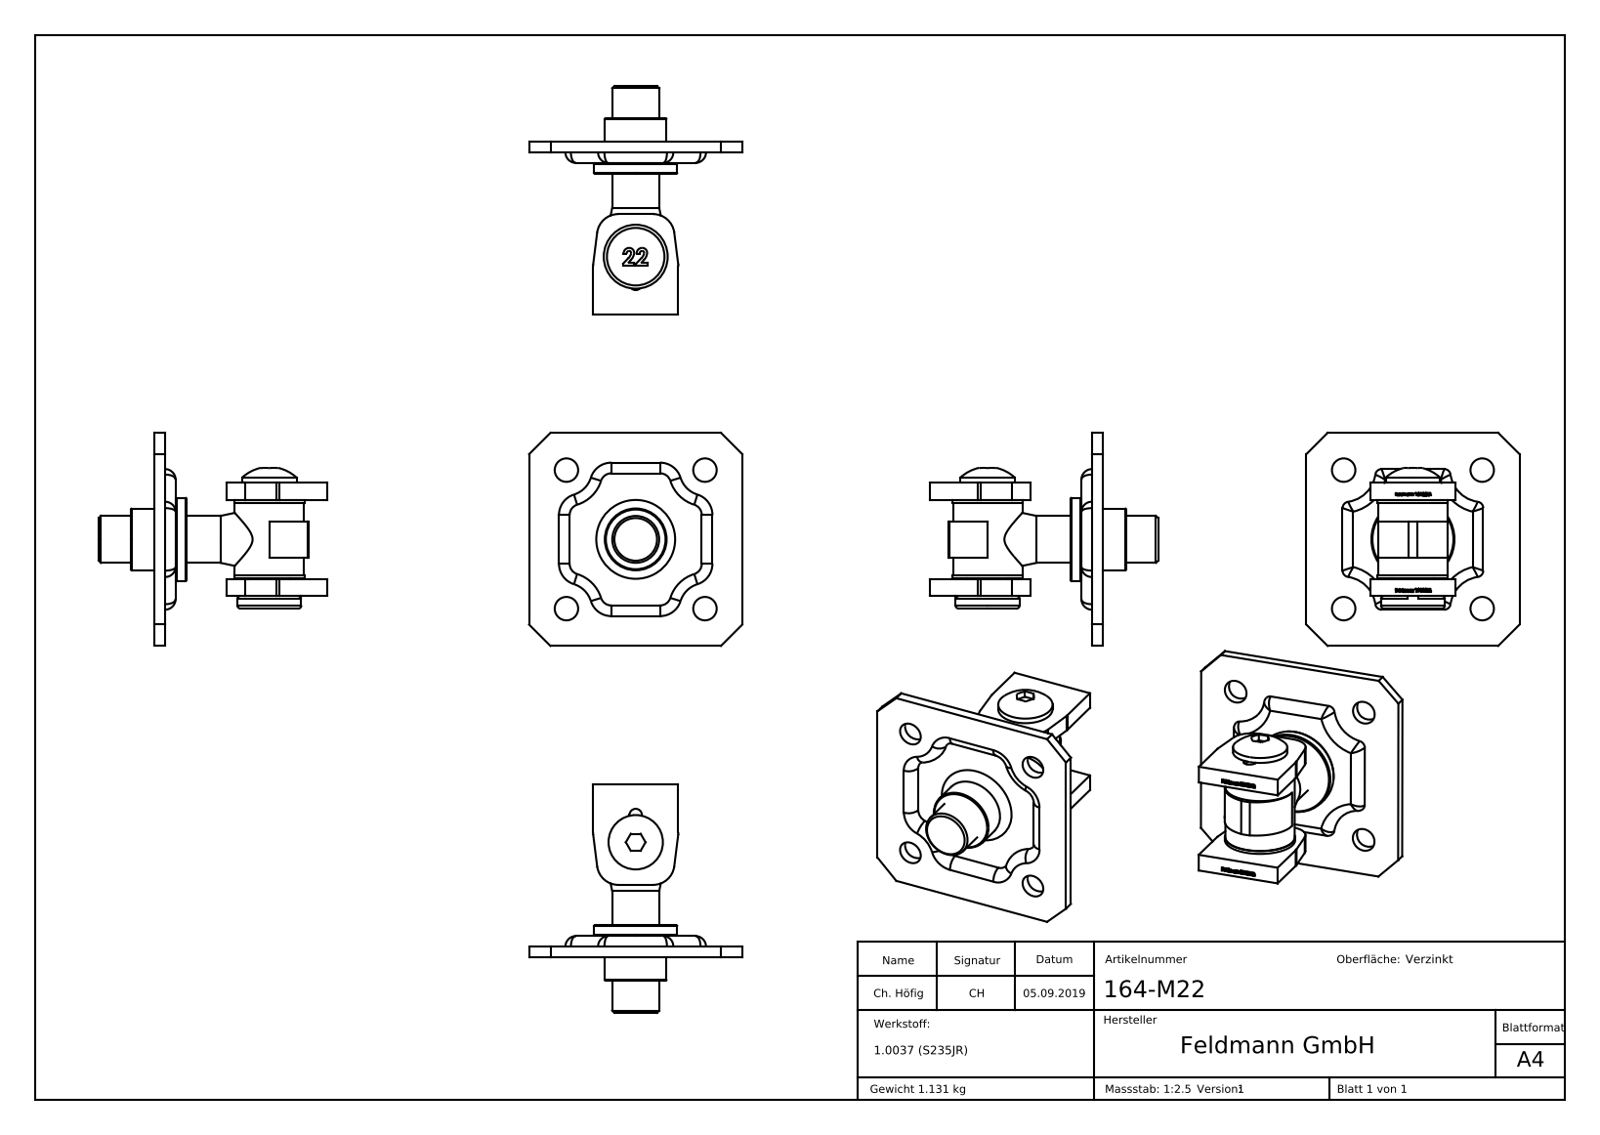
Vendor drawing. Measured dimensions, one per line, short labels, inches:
name: 164-MXX Teil2_164-M22 Teil2; 164-MXX Teil4_164-M22 Teil4; 164-MXX Teil1_164-M22 Teil1; 164-MXX Teil5_164-M22 Teil5 (+3 more)
written by: SolidWorks 2015 (CONFIG_CONTROL_DESIGN)
unit: in
bodies: 8 solids, 598 faces (326 planar, 68 cylindrical, 204 other)
size: 4.213 × 3.937 × 3.937
volume: 8.922 in³; area: 87.75 in²
holes: 4× ⌀0.433, 1× ⌀0.335, 1× ⌀0.472, 1× ⌀0.768, 1× ⌀0.787, 1× ⌀0.795, 1× ⌀0.866
bosses: 1× ⌀1.535, 1× ⌀1.457, 1× ⌀1.299, 1× ⌀1.28, 1× ⌀1.181, 1× ⌀1.142, 1× ⌀1.004, 1× ⌀0.866
rounds: 8× R0.197, 5× R0.394, 2× R0.709, 1× R0.114
face distances: 0.197, 1.772, 0.315, 1.713, 0.374, 0.059, 1.398, 2.087, 0.394, 1.457
hole spacings: 1.809, 2.559, 3.619
